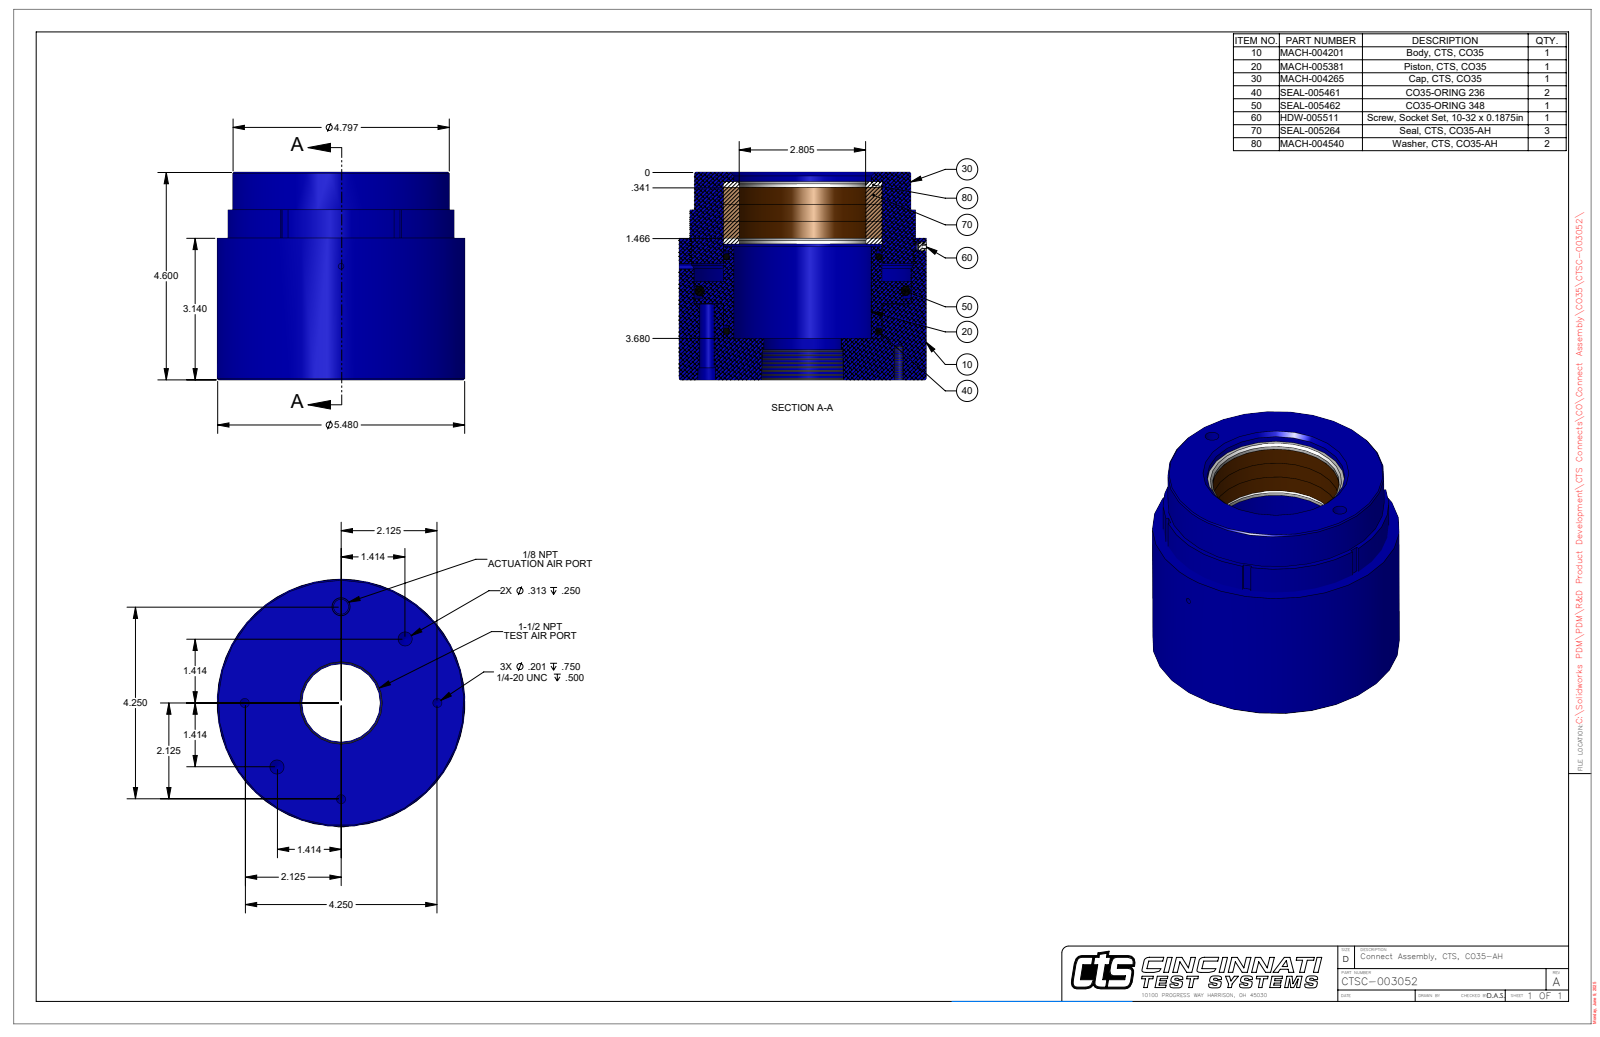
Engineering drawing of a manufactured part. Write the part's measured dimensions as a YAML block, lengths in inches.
part_name: "CTSC-003052"
step_written_by: "SolidWorks 2023 (AUTOMOTIVE_DESIGN)"
units: inches
bodies: {solids: 2, faces: 132, planar: 50, cylindrical: 58, other: 24}
overall_size: [5.486, 5.48, 4.6]
volume: 73.44
surface_area: 178.7
round_holes:
  - {diameter: 0.313, count: 4}
  - {diameter: 0.201, count: 3}
  - {diameter: 0.125, count: 1}
  - {diameter: 0.332, count: 1}
  - {diameter: 1.719, count: 1}
  - {diameter: 2.805, count: 1}
  - {diameter: 2.807, count: 1}
  - {diameter: 3.05, count: 1}
  - {diameter: 3.084, count: 1}
  - {diameter: 3.517, count: 1}
round_bosses_or_shafts:
  - {diameter: 5.48, count: 1}
  - {diameter: 5, count: 1}
  - {diameter: 4.797, count: 1}
  - {diameter: 3.513, count: 1}
  - {diameter: 3.509, count: 1}
partial_cylinders:
  - {radius: 2.46, count: 1}
  - {radius: 2.724, count: 1}
face_to_face_distances: [4.6, 4.259, 0.341, 0.125, 4.384, 0.216, 0.92, 3.339, 3.464, 3.68]
hole_center_spacings: [1.583, 2, 2.125, 2.918, 3.005, 3.811, 0.125, 1.531]
